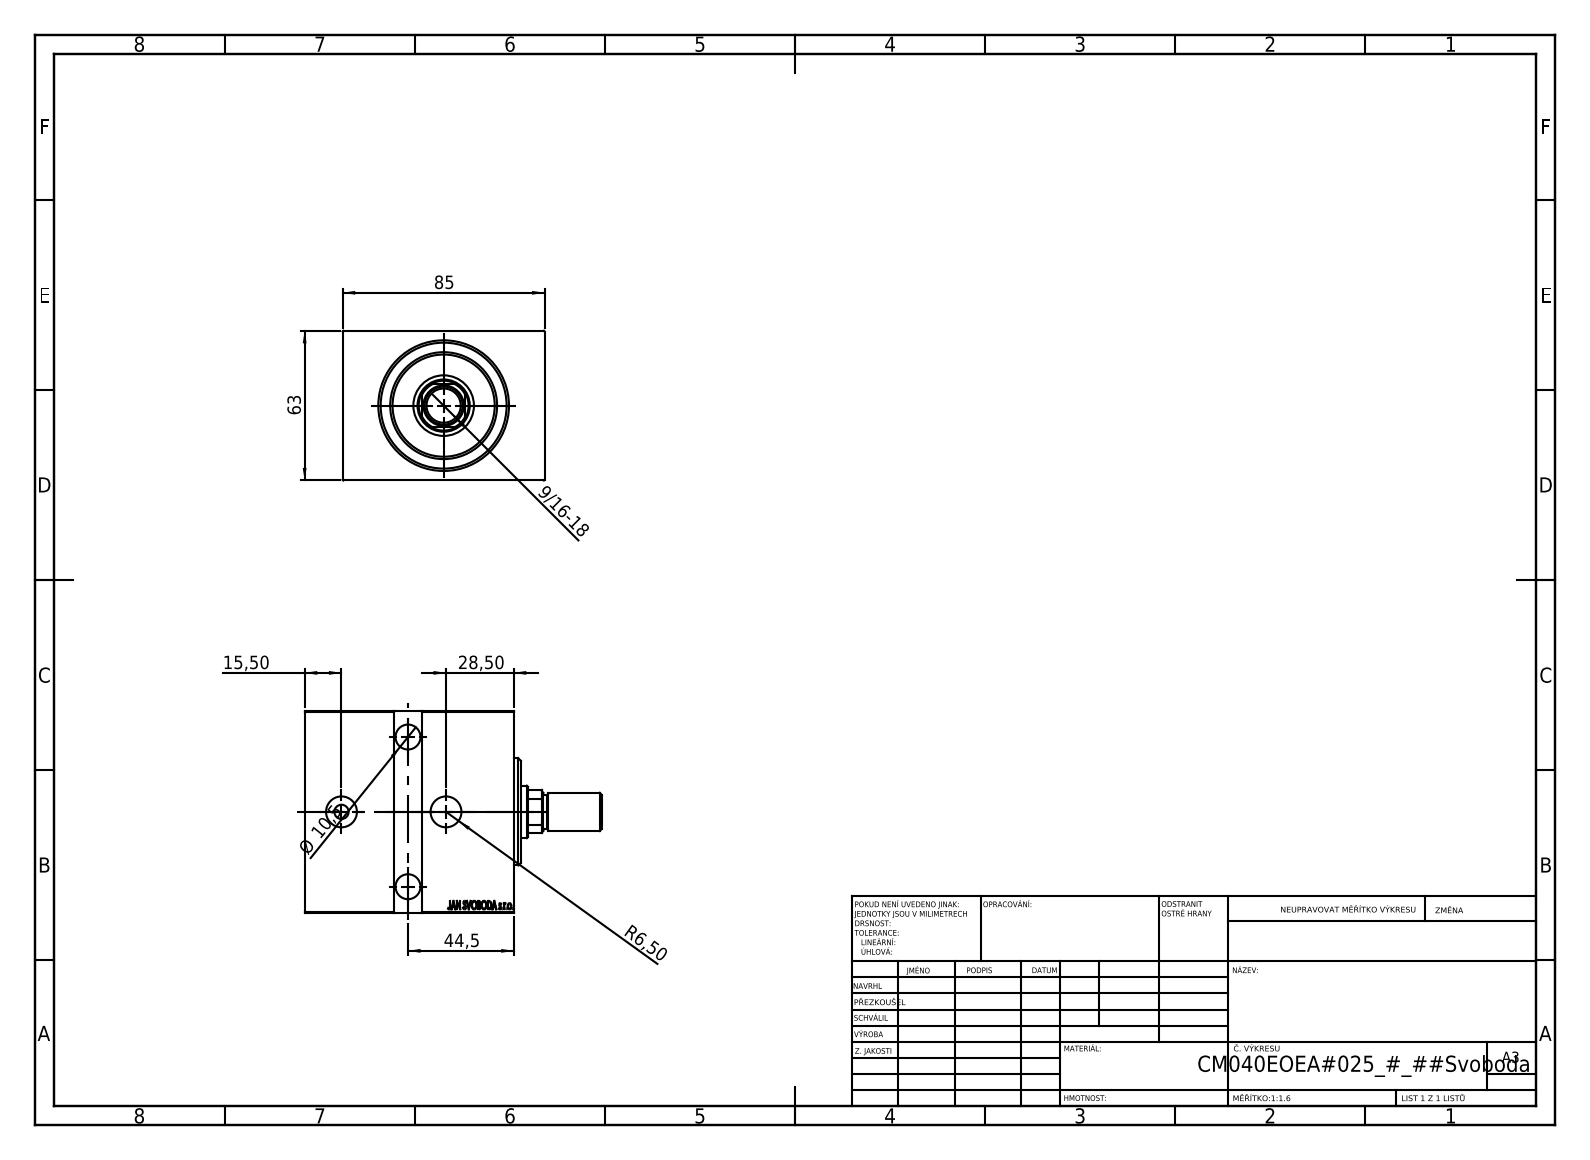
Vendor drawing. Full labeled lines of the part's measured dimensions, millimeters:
Part name (STEP PRODUCT): V450CM_E_Body; V450CM_VC_B; V450CM_MALE_METRIC; V450CM_E_VCP
STEP written by: SolidWorks 2019 (CONFIG_CONTROL_DESIGN)
Units: millimetres
Bodies: 4 solids, 853 faces (411 planar, 42 cylindrical, 400 other)
Overall size (bounding box): 125 × 85 × 63
Volume: 448 022 mm³ · Surface area: 72 550 mm²
Round holes (diameter × count): ⌀10.5 ×2, ⌀13 ×2, ⌀16.5 ×2, ⌀12.5 ×1, ⌀22 ×1, ⌀25.5 ×1, ⌀40 ×1, ⌀53 ×1
Round bosses / shafts (diameter × count): ⌀45 ×1, ⌀42 ×1, ⌀16 ×1, ⌀14 ×1, ⌀6 ×1
Partial cylindrical surfaces — rounded edges, fillets, slot ends (radius × count): R10.5 ×1
Main face-to-face distances: 63, 85, 88, 12, 76, 3, 5, 83, 71, 18
Hole centre spacings: 35.33, 42.15, 44, 63
